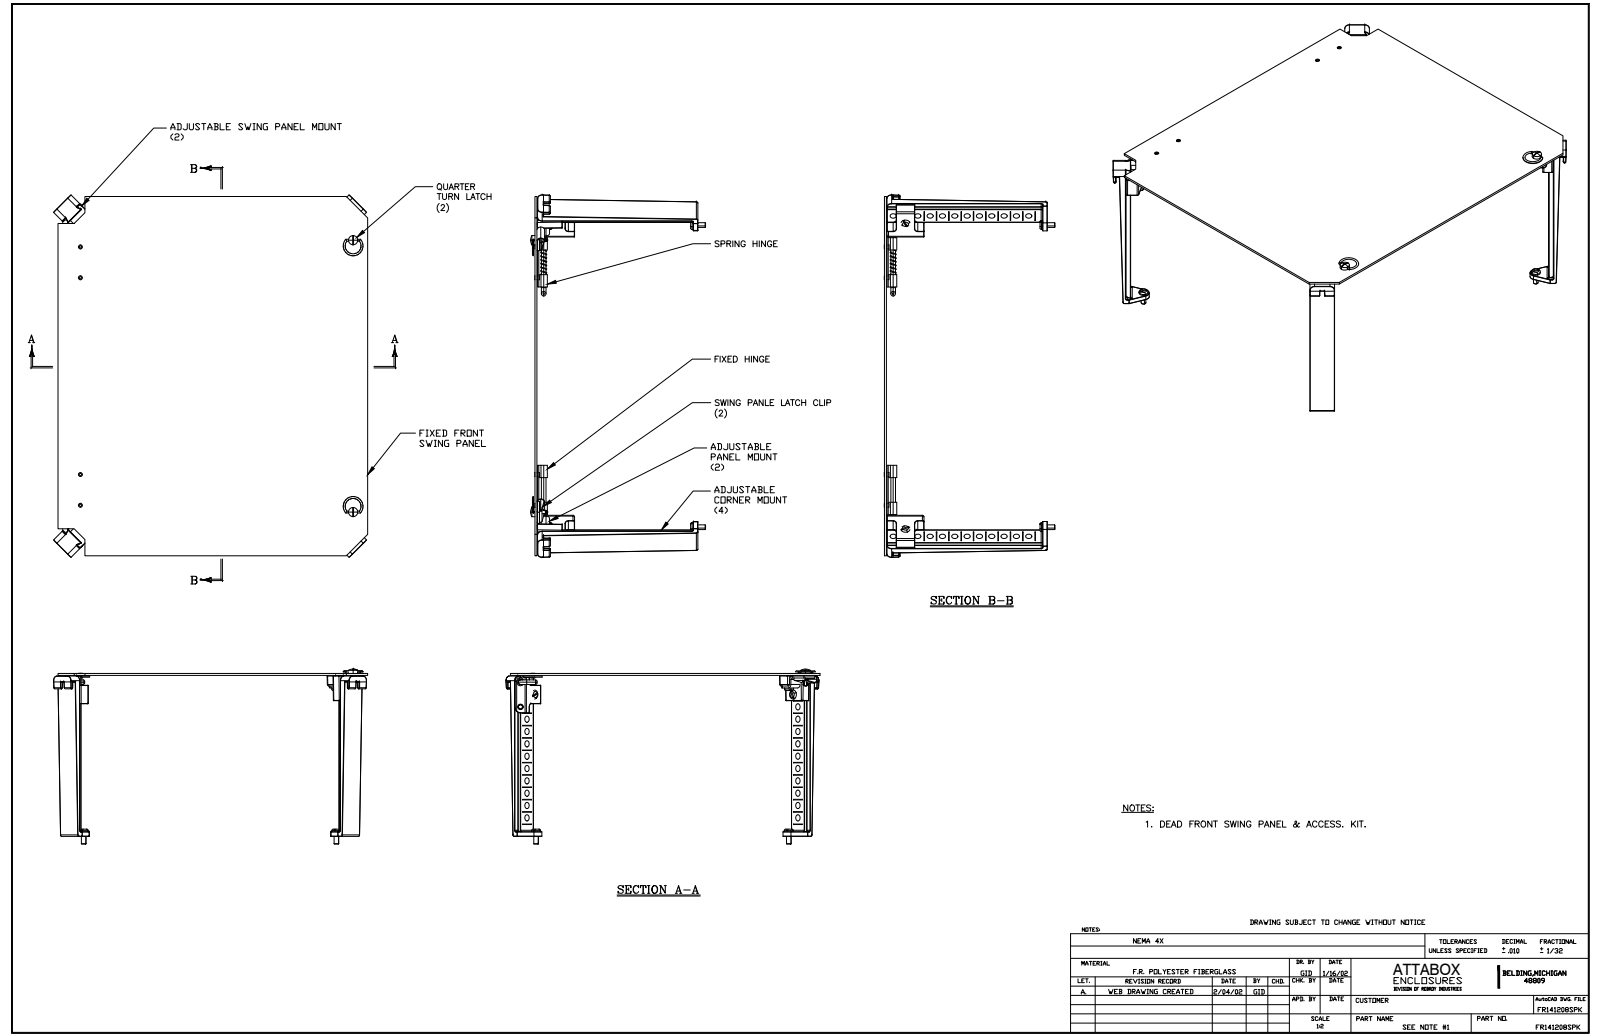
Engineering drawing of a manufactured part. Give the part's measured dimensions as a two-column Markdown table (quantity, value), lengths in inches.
| quantity | value |
| --- | --- |
| part name | FR141208SPK |
| STEP written by | SolidWorks 2019 (AUTOMOTIVE_DESIGN) |
| units | inches |
| bodies | 48 solids, 2225 faces (1070 planar, 493 cylindrical, 662 other) |
| overall size | 14.688 × 12.749 × 7.183 |
| volume | 26.14 in³ |
| surface area | 525.7 in² |
| round holes (diameter × count) | 0.25 × 52, 0.156 × 6, 0.253 × 6, 0.05 × 4, 0.14 × 4, 0.144 × 4, 0.217 × 4, 0.22 × 4, 0.312 × 3, 0.197 × 2, 0.35 × 2, 0.153 × 1 |
| round bosses / shafts (diameter × count) | 0.19 × 10, 0.373 × 6, 0.246 × 6, 0.433 × 4, 0.315 × 4, 0.16 × 4, 0.079 × 4, 0.394 × 2 |
| partial cylindrical surfaces (radius × count) | 0.01 × 212, 0.06 × 44, 0.063 × 14, 0.025 × 8, 0.13 × 6, 0.049 × 4, 0.062 × 4, 0.19 × 4 |
| main face-to-face distances | 0.08, 16.951, 0.203, 17.154, 1, 1.414, 8.472, 8.886, 8.269, 8.683 |
| hole center spacings | 1.5, 0.5, 1, 1.732, 2.061, 2, 2.45, 2.5 |
